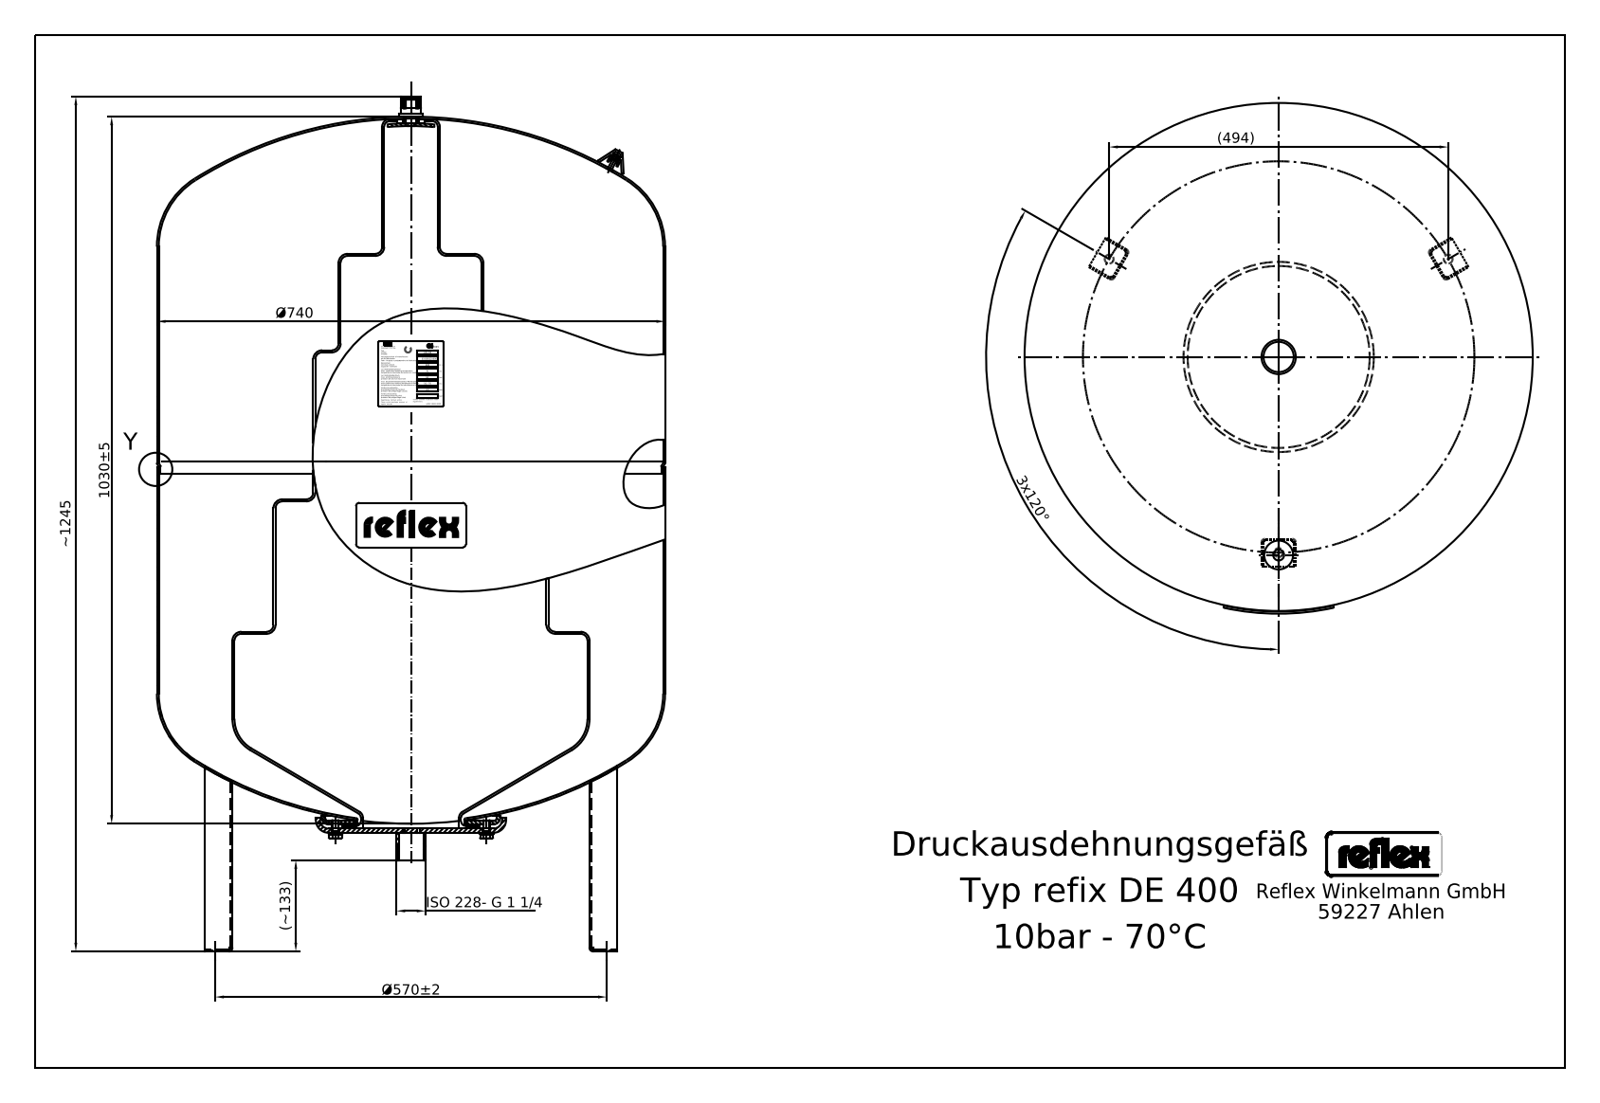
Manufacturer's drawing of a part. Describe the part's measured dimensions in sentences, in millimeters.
Its 3-D file was written by "Mechanical Desktop 2008 (CONFIG_CONTROL_DESIGN)". It is 17 solids with 394 faces: 181 planar, 139 cylindrical and 74 other. Overall it measures 1245 by 740 by 740 millimeters. Its volume is 388 000 000 cubic millimeters and its surface area 4 879 000 square millimeters. Round holes: 3 of diameter 13.4, 1 of diameter 14.1, 1 of diameter 157, 1 of diameter 250. Round bosses or shafts: 8 of diameter 10, 1 of diameter 740, 1 of diameter 260, 1 of diameter 230, 1 of diameter 42.4, 1 of diameter 34, 1 of diameter 17.1, 1 of diameter 16. Partial cylindrical surfaces (rounded edges, fillets, slot ends): 15 of radius 1, 15 of radius 2.5, 15 of radius 5, 4 of radius 5.62, 3 of radius 2.25, 2 of radius 3.84, 2 of radius 6.75, 2 of radius 9.27. The main face-to-face distances are 652, 2.5, 47.5, 196, 848, 6, 202, 854, 45, 50. The hole center spacings are 285, 493.64.
